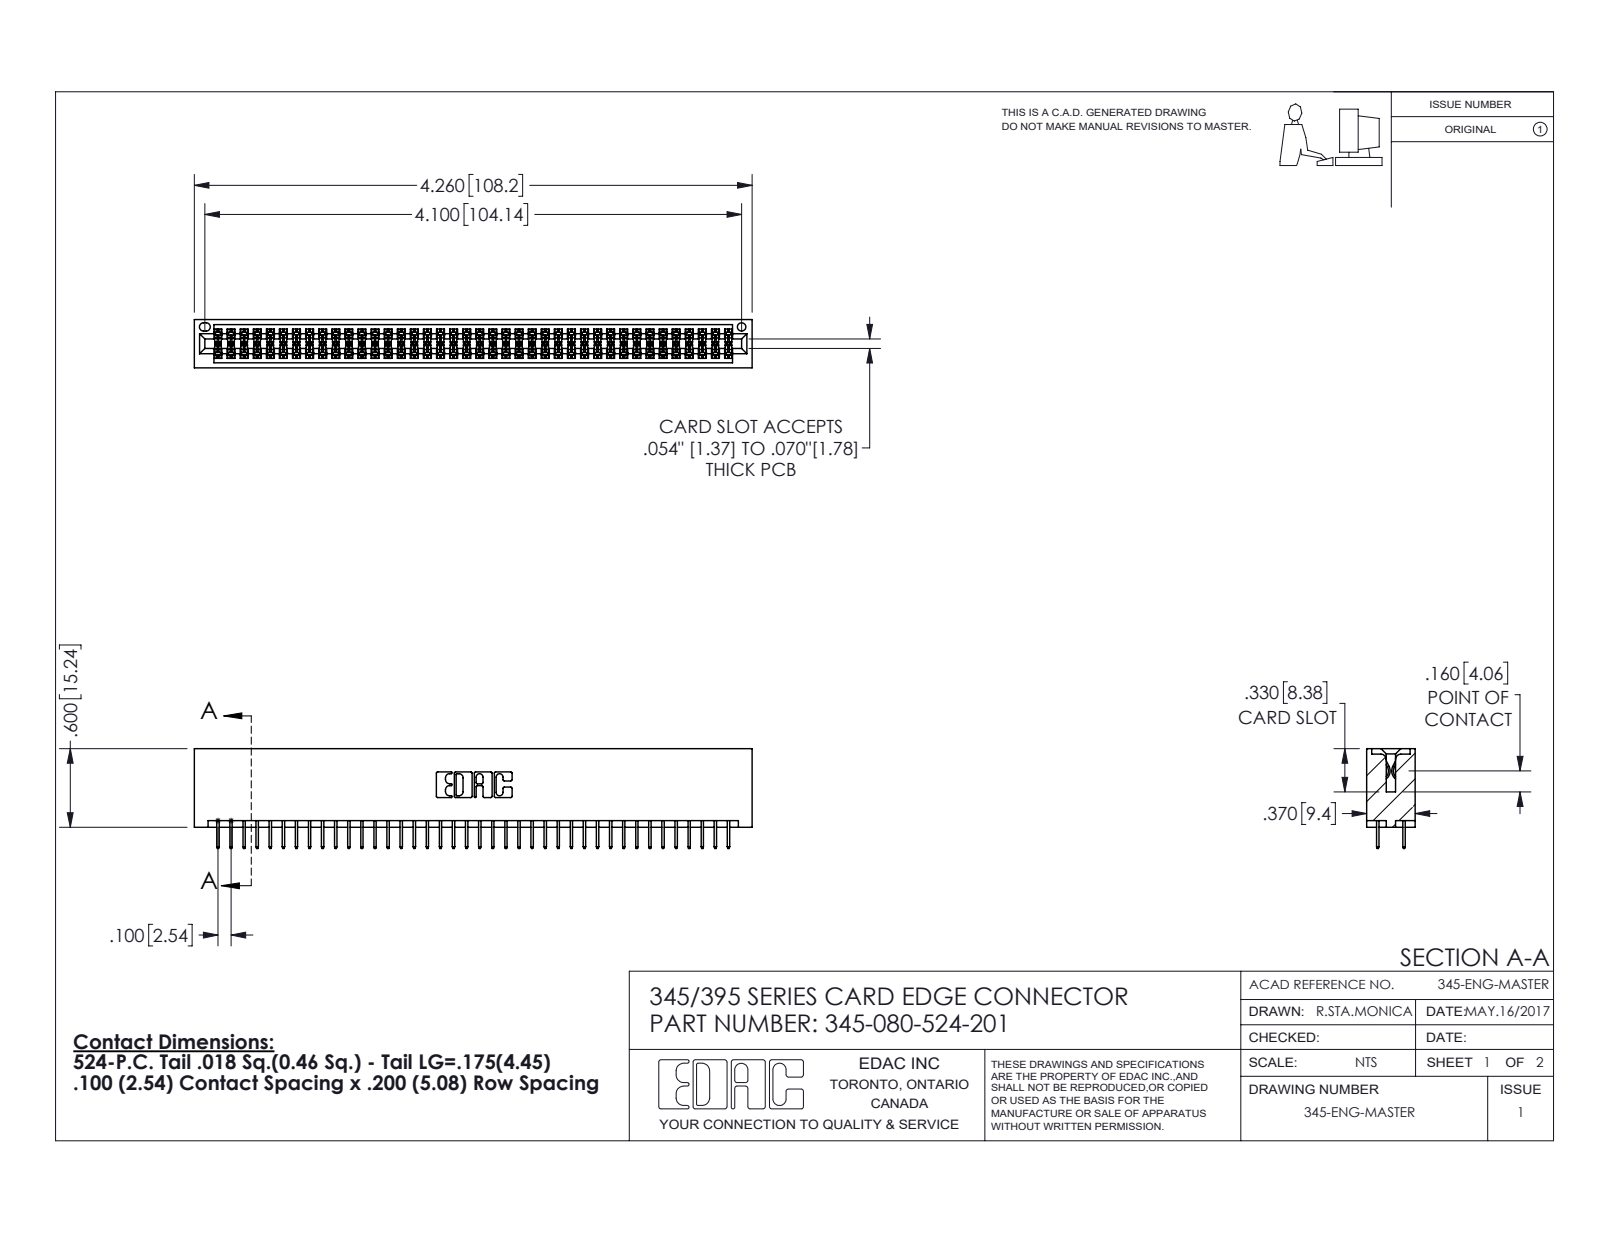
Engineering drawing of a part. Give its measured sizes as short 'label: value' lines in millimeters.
name: 345-080-524-201; 345-292-001_345-293-124; 345 Part_No Mounting Lugs
written by: SolidWorks 2016 (CONFIG_CONTROL_DESIGN)
unit: mm
bodies: 81 solids, 4438 faces (3196 planar, 1242 cylindrical, 0 other)
size: 108.2 × 19.4 × 9.4
volume: 11 000 mm³; area: 16 190 mm²
holes: 1× ⌀1.6
rounds: 120× R0.2, 22× R0.3, 6× R0.2, 6× R0.8, 3× R0.7, 2× R0.4, 2× R0.5, 2× R0.6
face distances: 7.6, 1.8, 5.1, 9.4, 2.5, 6.9, 0.6, 5.7, 1.8, 4.4
